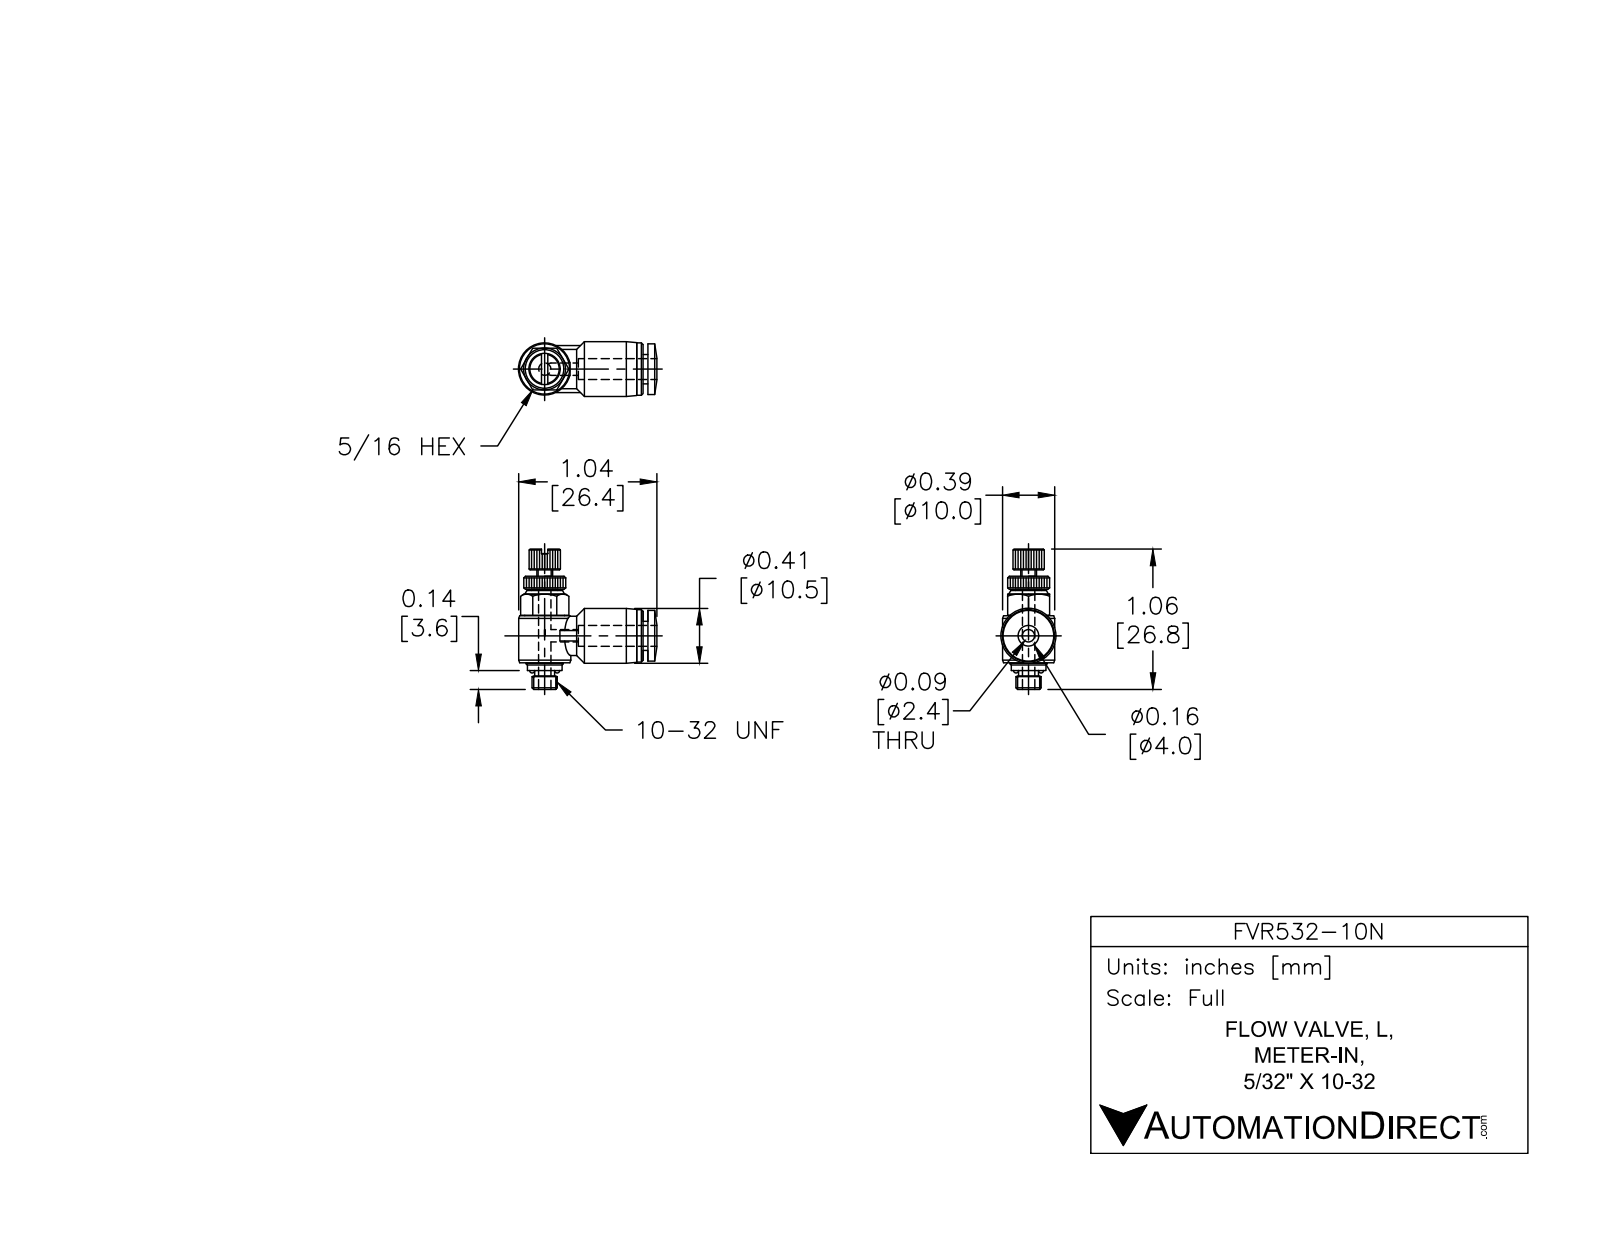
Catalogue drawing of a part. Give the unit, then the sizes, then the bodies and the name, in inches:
Units: inches
Overall size (bounding box): 1.146 × 0.998 × 0.413
Round holes (diameter × count): ⌀0.059 ×2, ⌀0.15 ×1, ⌀0.169 ×1
Round bosses / shafts (diameter × count): ⌀0.394 ×2, ⌀0.413 ×1, ⌀0.388 ×1, ⌀0.299 ×1, ⌀0.28 ×1, ⌀0.265 ×1, ⌀0.264 ×1, ⌀0.26 ×1
Partial cylindrical surfaces — rounded edges, fillets, slot ends (radius × count): R0.118 ×1, R0.157 ×1
Main face-to-face distances: 0.315, 0.037, 0.652, 0.354, 0.206, 0.293, 0.297, 0.156, 0.555, 0.553
Volume: 0.136 in³ · Surface area: 2.98 in²
Bodies: 2 solids, 345 faces (149 planar, 97 cylindrical, 99 other)
Part name (STEP PRODUCT): FVR532-10N
STEP written by: SolidWorks 2015 (AUTOMOTIVE_DESIGN)
